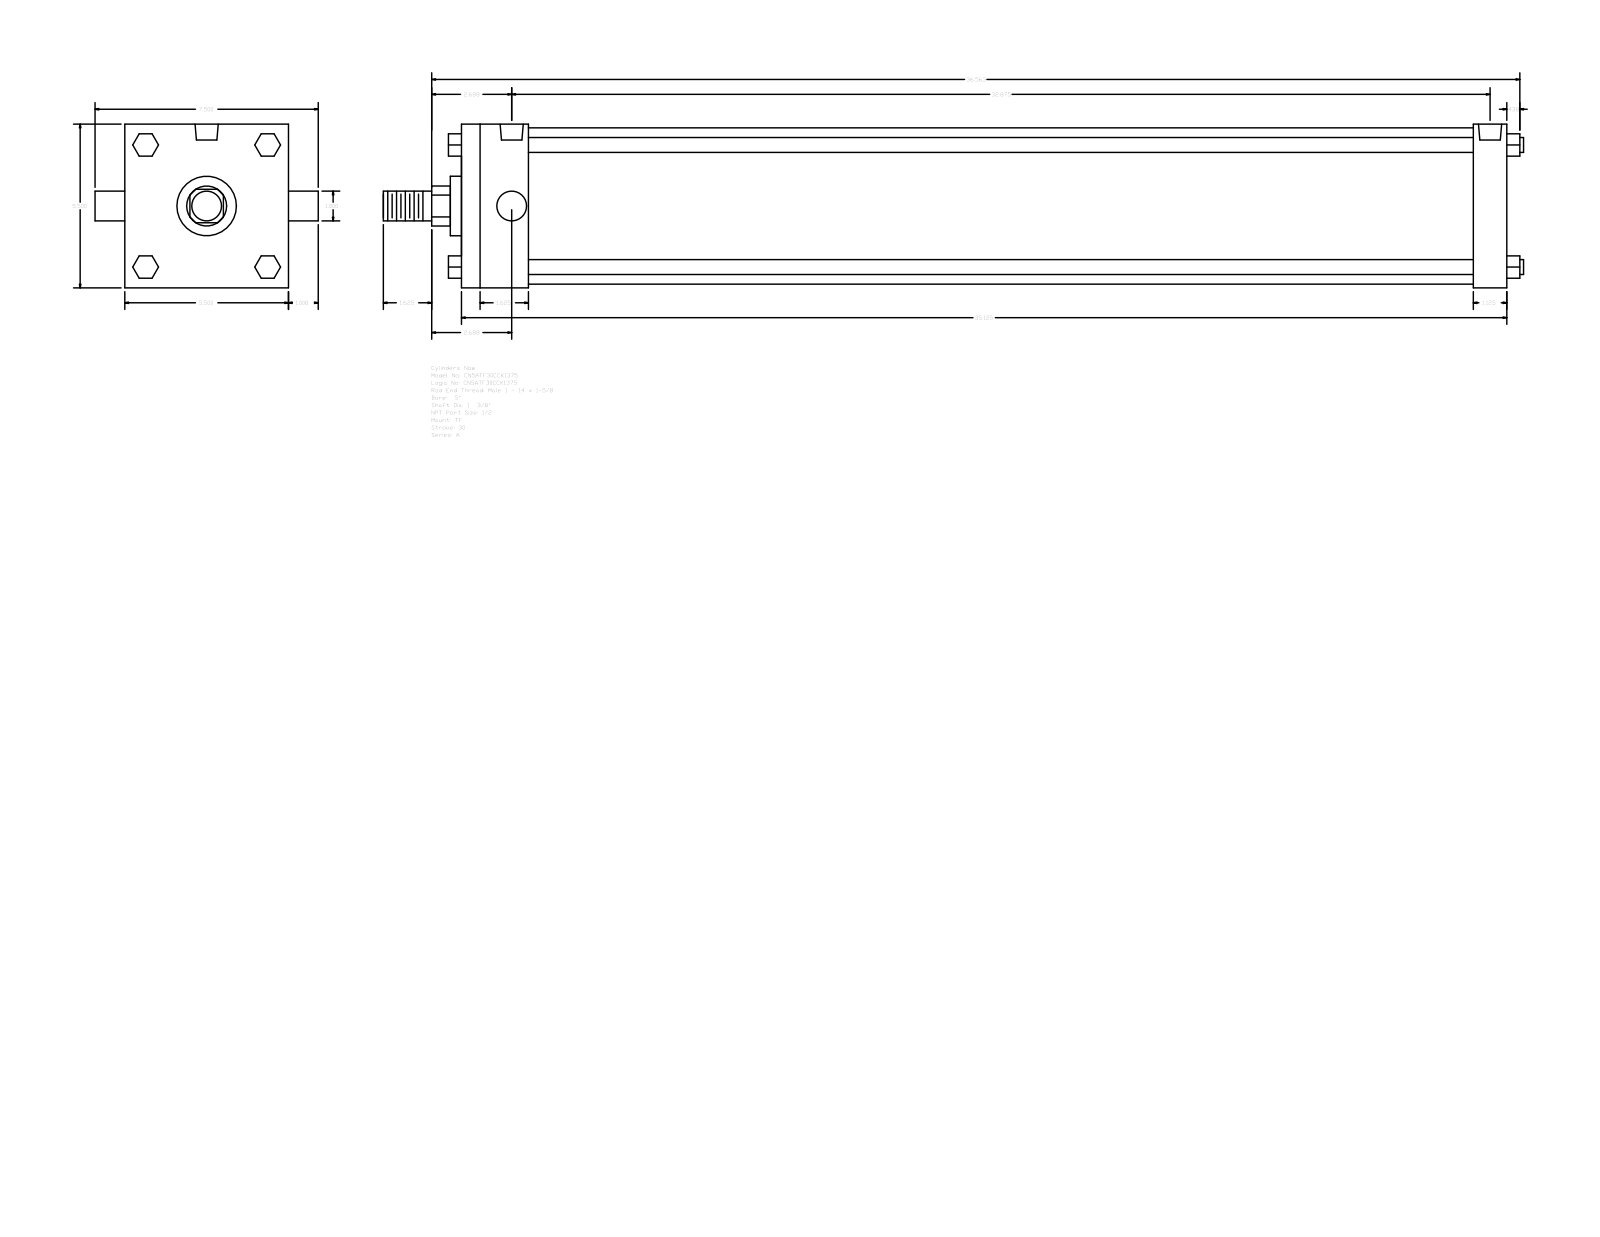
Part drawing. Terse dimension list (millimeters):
name: A_TF__0500_1.375
written by: GSSL Pune (CONFIG_CONTROL_DESIGN)
unit: mm
bodies: 0 solids, 120 faces (92 planar, 28 cylindrical, 0 other)
size: 973.14 × 190.5 × 139.7
holes: 3× ⌀8.73, 2× ⌀19.77
bosses: 4× ⌀12.7, 2× ⌀25.4, 1× ⌀133.35, 1× ⌀50.8, 1× ⌀34.92
rounds: 1× R17.06
face distances: 139.7, 892.18, 57.15, 28.58, 863.6, 806.45, 835.03, 19.05, 52.07, 90.18
hole spacings: 2.39, 832.64, 830.25, 835.03
